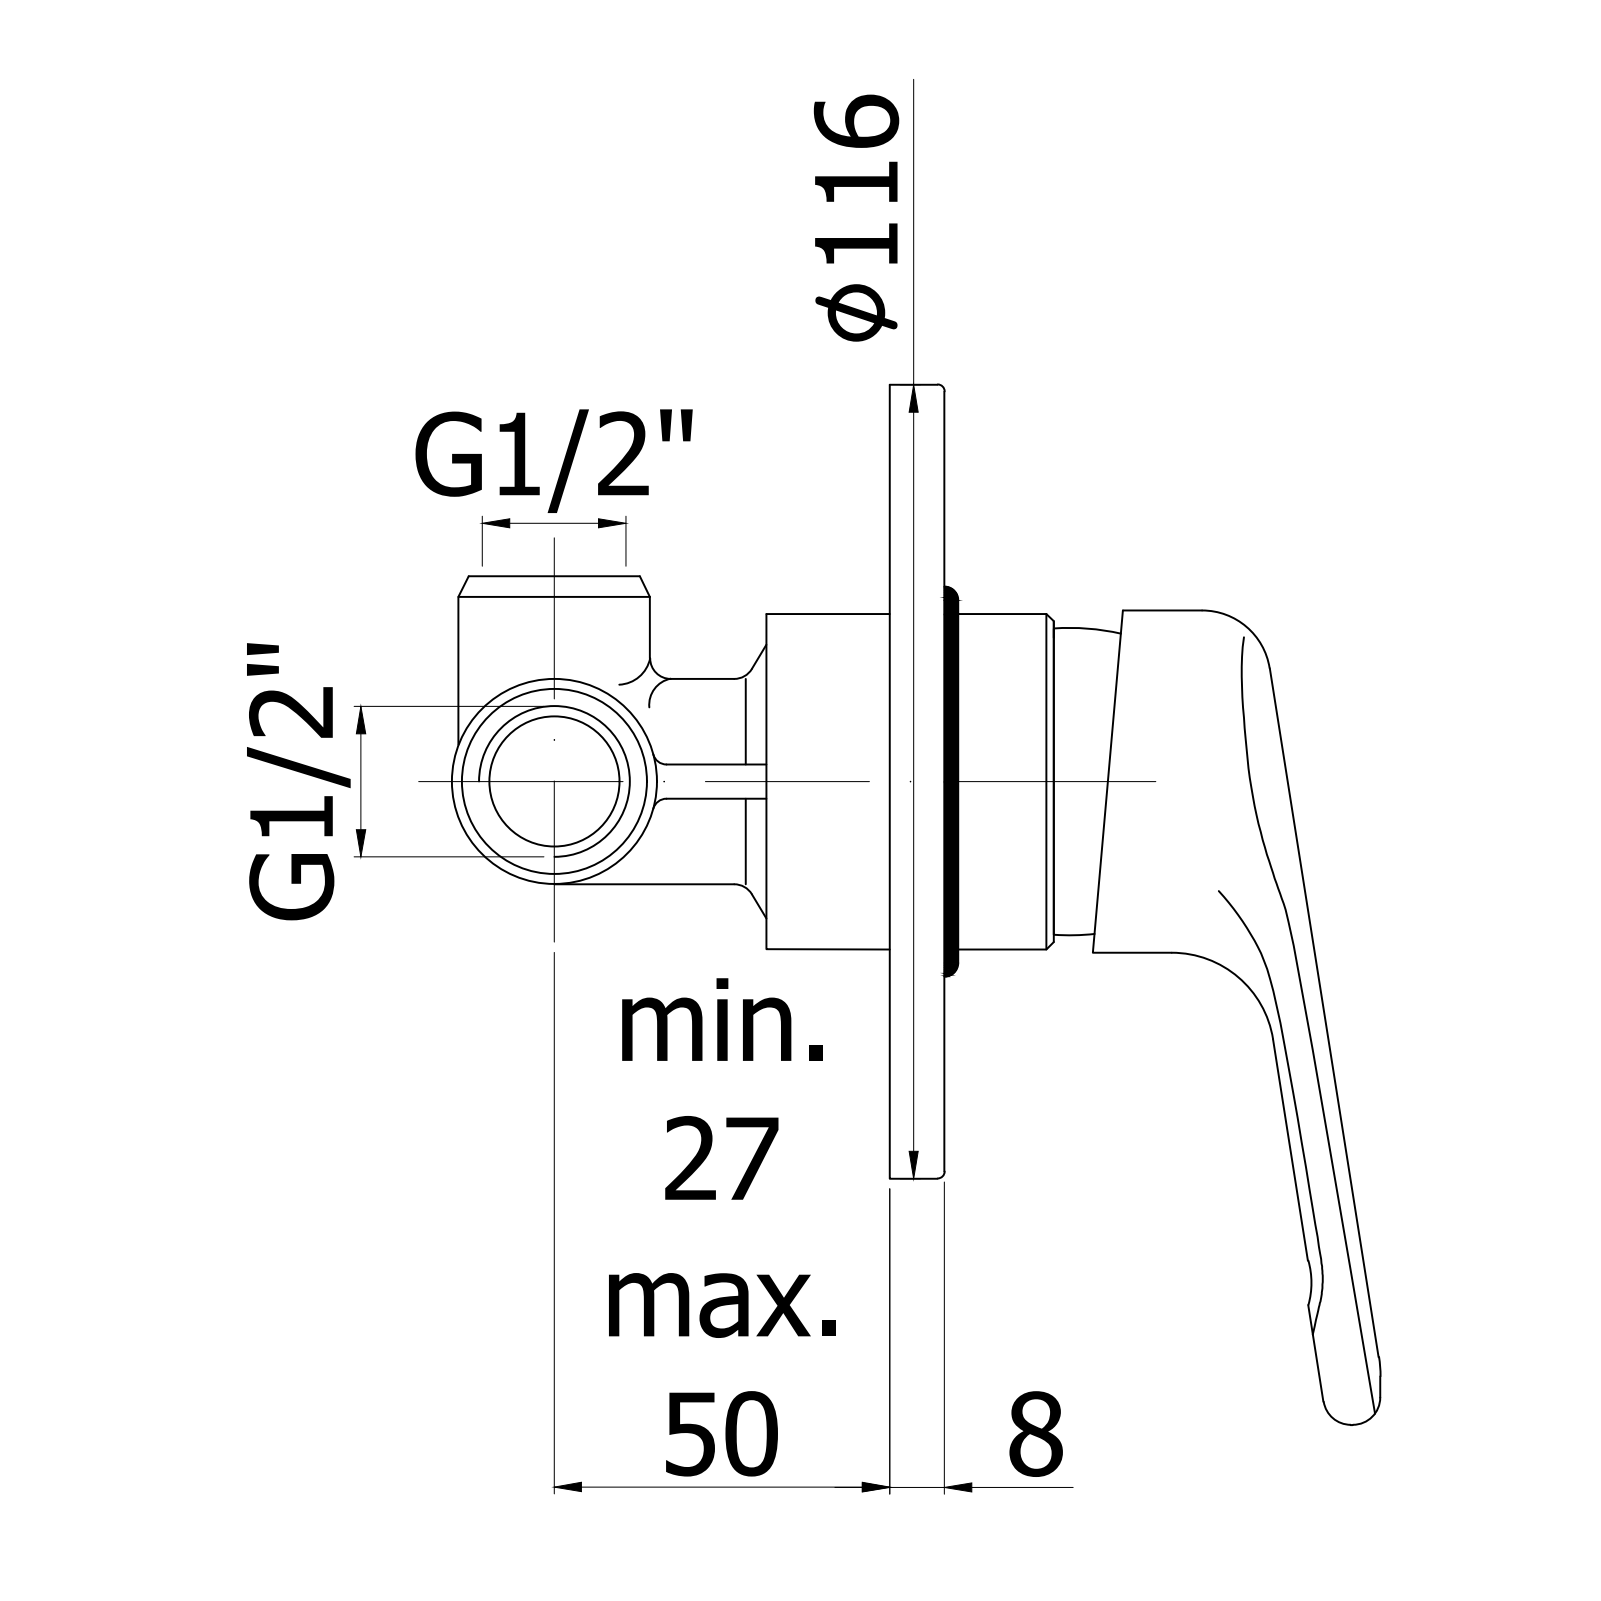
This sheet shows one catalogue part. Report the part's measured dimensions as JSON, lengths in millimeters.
{"part_name": "NT010CR", "step_written_by": "CREO PARAMETRIC BY PTC INC, 2020044 (CONFIG_CONTROL_DESIGN)", "units": "millimeters", "bodies": {"solids": 1, "faces": 907, "planar": 494, "cylindrical": 240, "other": 173}, "overall_size": [151.68, 116, 80.74], "volume_mm3": 91295, "surface_area_mm2": 71254, "round_holes": [[8, 2], [3, 1], [3.3, 1], [4, 1], [4.5, 1], [5, 1], [6, 1], [9.4, 1], [11, 1], [21, 1], [21.2, 1], [26.1, 1]], "round_bosses_or_shafts": [[50, 2], [116, 1], [56.5, 1], [55, 1], [39.5, 1], [36.7, 1], [33, 1], [25.8, 1]], "partial_cylinders_radius": [[0.2, 24], [0.5, 22], [1, 5], [2, 4], [135, 2], [2.5, 1], [3.9, 1], [7, 1]], "face_to_face_distances": [2.6, 20.9, 12.5, 5, 18.3, 7.95, 2.95, 23.5, 13, 24], "hole_center_spacings": [9.9, 9.92, 14.76, 5.97, 6, 14]}
